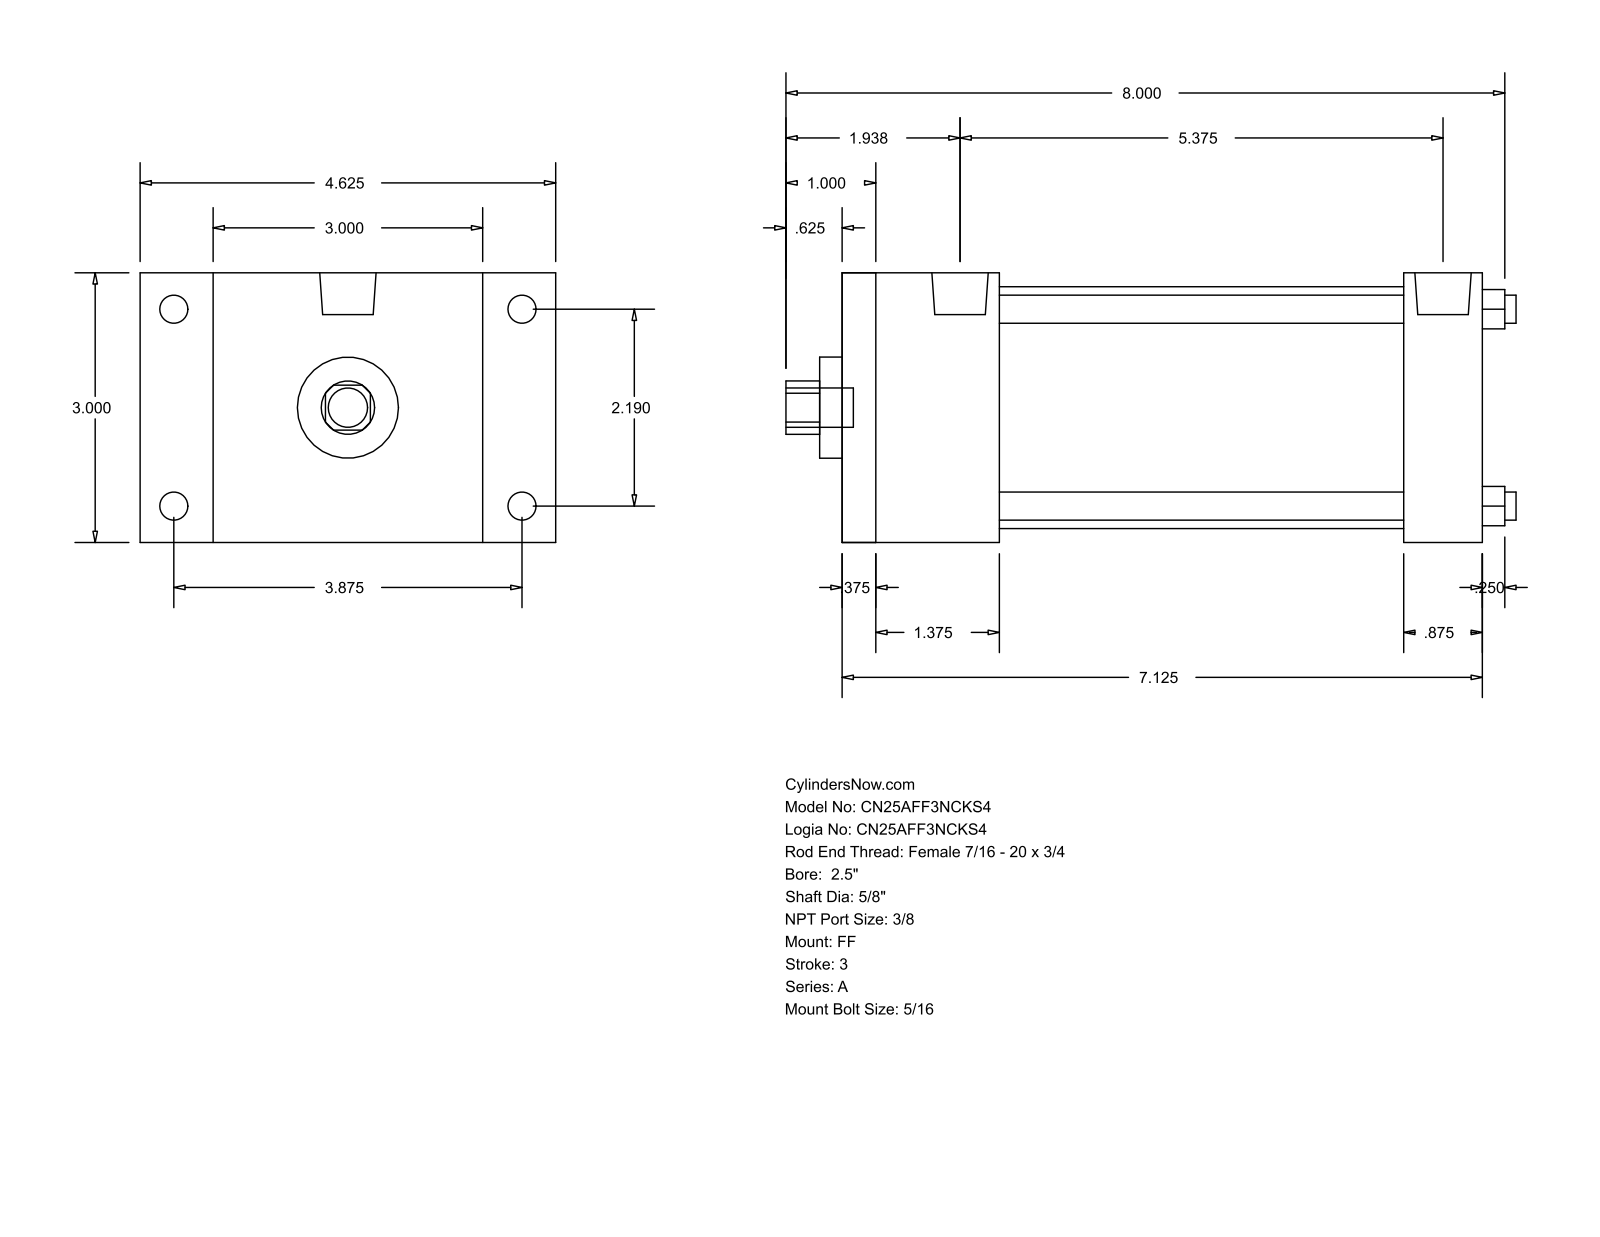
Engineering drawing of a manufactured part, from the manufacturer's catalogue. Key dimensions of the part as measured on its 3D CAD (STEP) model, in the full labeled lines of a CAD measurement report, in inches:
Part name (STEP PRODUCT): A_FF__0250_0.625
STEP written by: GSSL Pune (CONFIG_CONTROL_DESIGN)
Units: inches
Bodies: 0 solids, 92 faces (64 planar, 28 cylindrical, 0 other)
Overall size (bounding box): 8.125 × 4.625 × 3
Round holes (diameter × count): ⌀0.313 ×4, ⌀0.625 ×1, ⌀1.125 ×1, ⌀2.69 ×1
Round bosses / shafts (diameter × count): ⌀0.313 ×4, ⌀0.219 ×4, ⌀0.627 ×2, ⌀0.437 ×1
Partial cylindrical surfaces — rounded edges, fillets, slot ends (radius × count): R0.297 ×1
Main face-to-face distances: 3, 7.125, 0.375, 6.75, 1.75, 6.25, 1.375, 5.875, 4.5, 5.375
Hole centre spacings: 1.548, 2.19, 3.097
